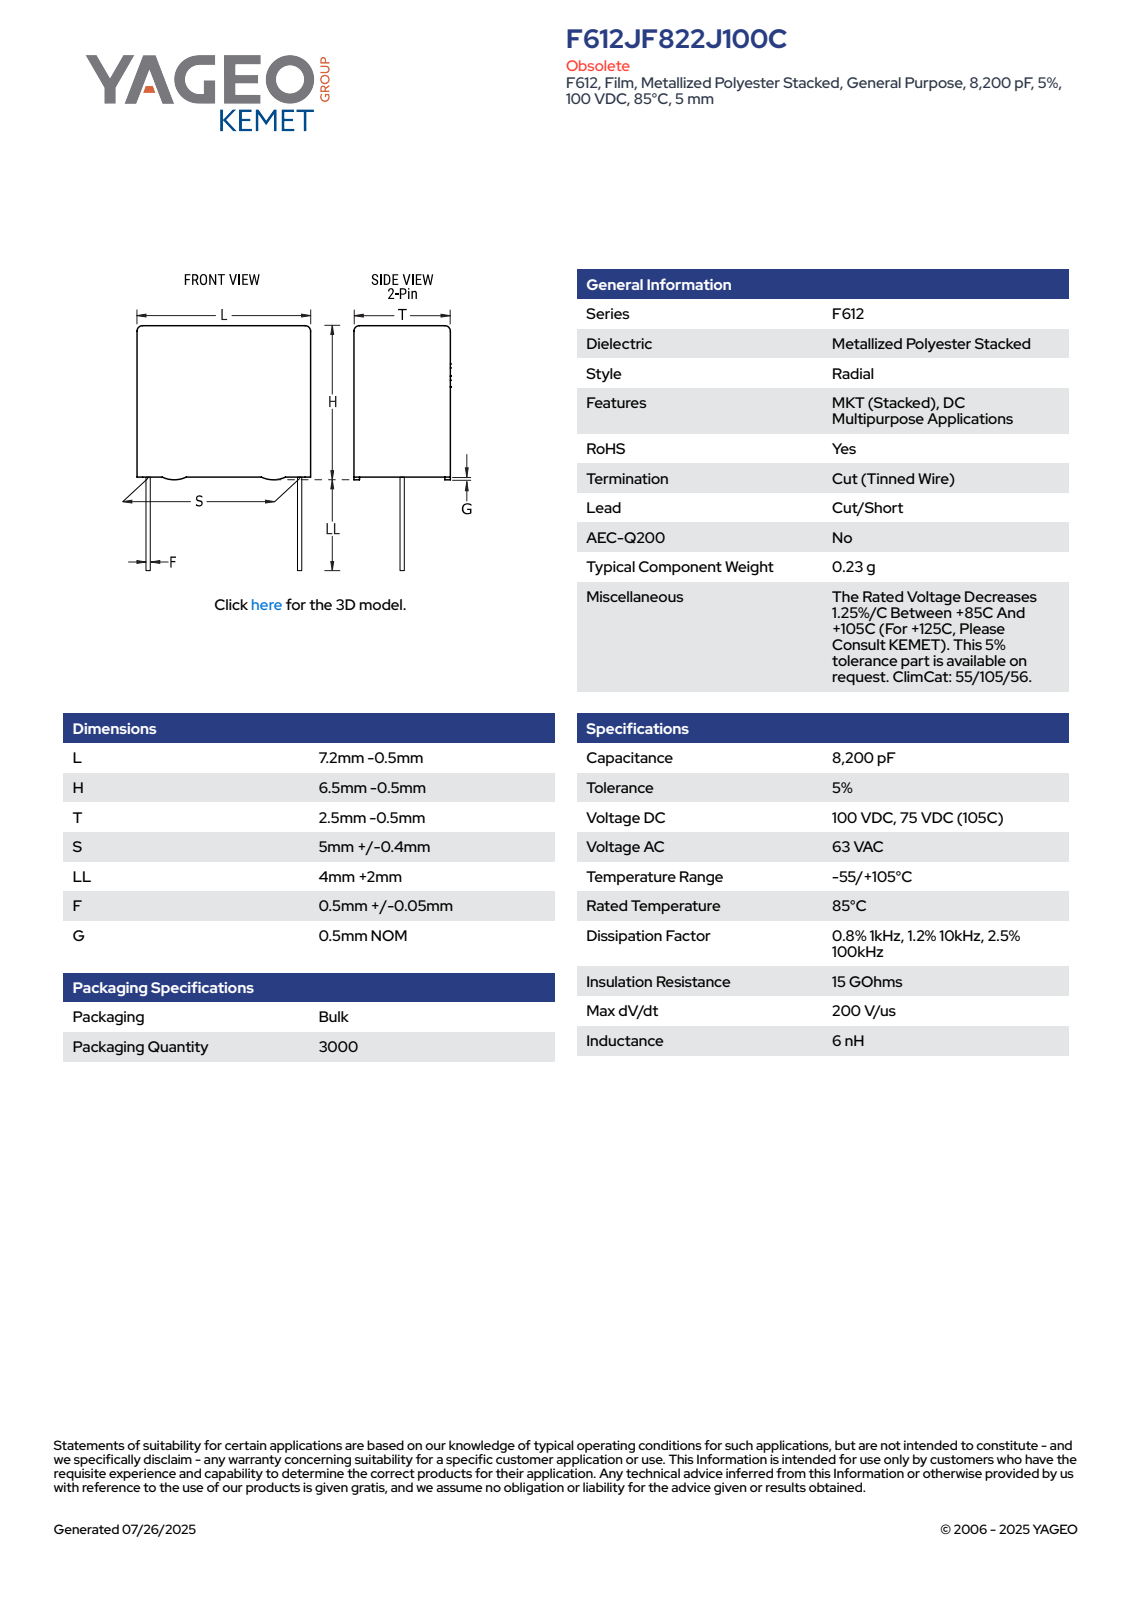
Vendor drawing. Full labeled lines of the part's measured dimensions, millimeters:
Part name (STEP PRODUCT): CFR_RBG_7.2X6.5X2.5_L6.7H6T2S5LL6F0.55G0.5
STEP written by: SolidWorks 2021 (AUTOMOTIVE_DESIGN)
Units: millimetres
Bodies: 4 solids, 89 faces (81 planar, 8 cylindrical, 0 other)
Overall size (bounding box): 12 × 6.7 × 2
Volume: 76 mm³ · Surface area: 151 mm²
Round bosses / shafts (diameter × count): ⌀0.55 ×2
Partial cylindrical surfaces — rounded edges, fillets, slot ends (radius × count): R0.5 ×4
Main face-to-face distances: 2, 6.7, 5.5, 1.89, 1.78, 6, 6.5, 12, 0.5, 2.49
